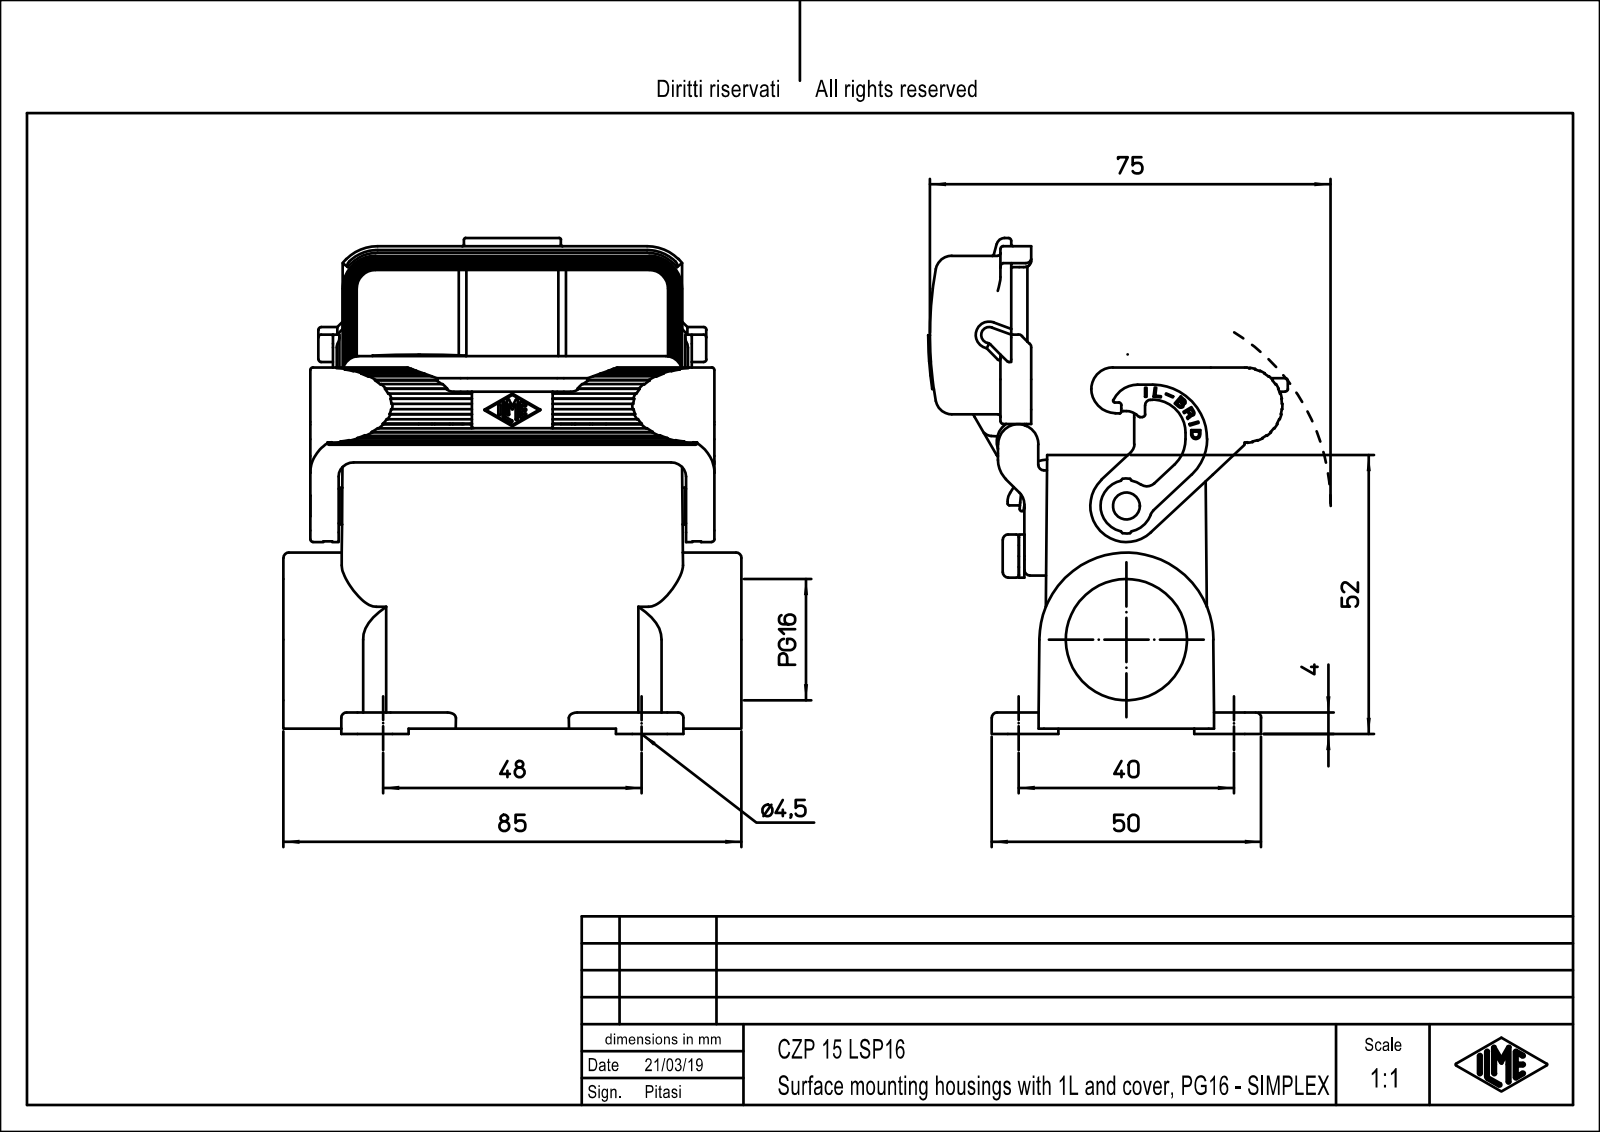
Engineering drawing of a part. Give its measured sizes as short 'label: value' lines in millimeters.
name: CZP_15_LSP16
written by: PTC Creo Elements/Direct Modeling 19.0E 27-Jun-2016 (C) Parametric Technology GmbH (AUTOMOTIVE_DESIGN)
unit: mm
bodies: 1 solid, 495 faces (289 planar, 186 cylindrical, 20 other)
size: 92.85 × 85 × 66.66
volume: 78 184 mm³; area: 46 900 mm²
holes: 4× ⌀3, 4× ⌀4.5, 1× ⌀5, 1× ⌀19, 1× ⌀22.5
bosses: 1× ⌀8.4, 1× ⌀8, 1× ⌀6.8, 1× ⌀4.8, 1× ⌀2.4
rounds: 13× R3, 7× R6.5, 4× R2, 4× R3.4, 4× R3.5, 4× R3.5, 4× R6.3, 3× R4
face distances: 2.6, 26.8, 24.2, 3, 29.4, 26.81, 6.4, 10.25, 74.75, 3.8
hole spacings: 12.02, 28.01, 50.21, 56.22, 16, 40, 48, 49.5
